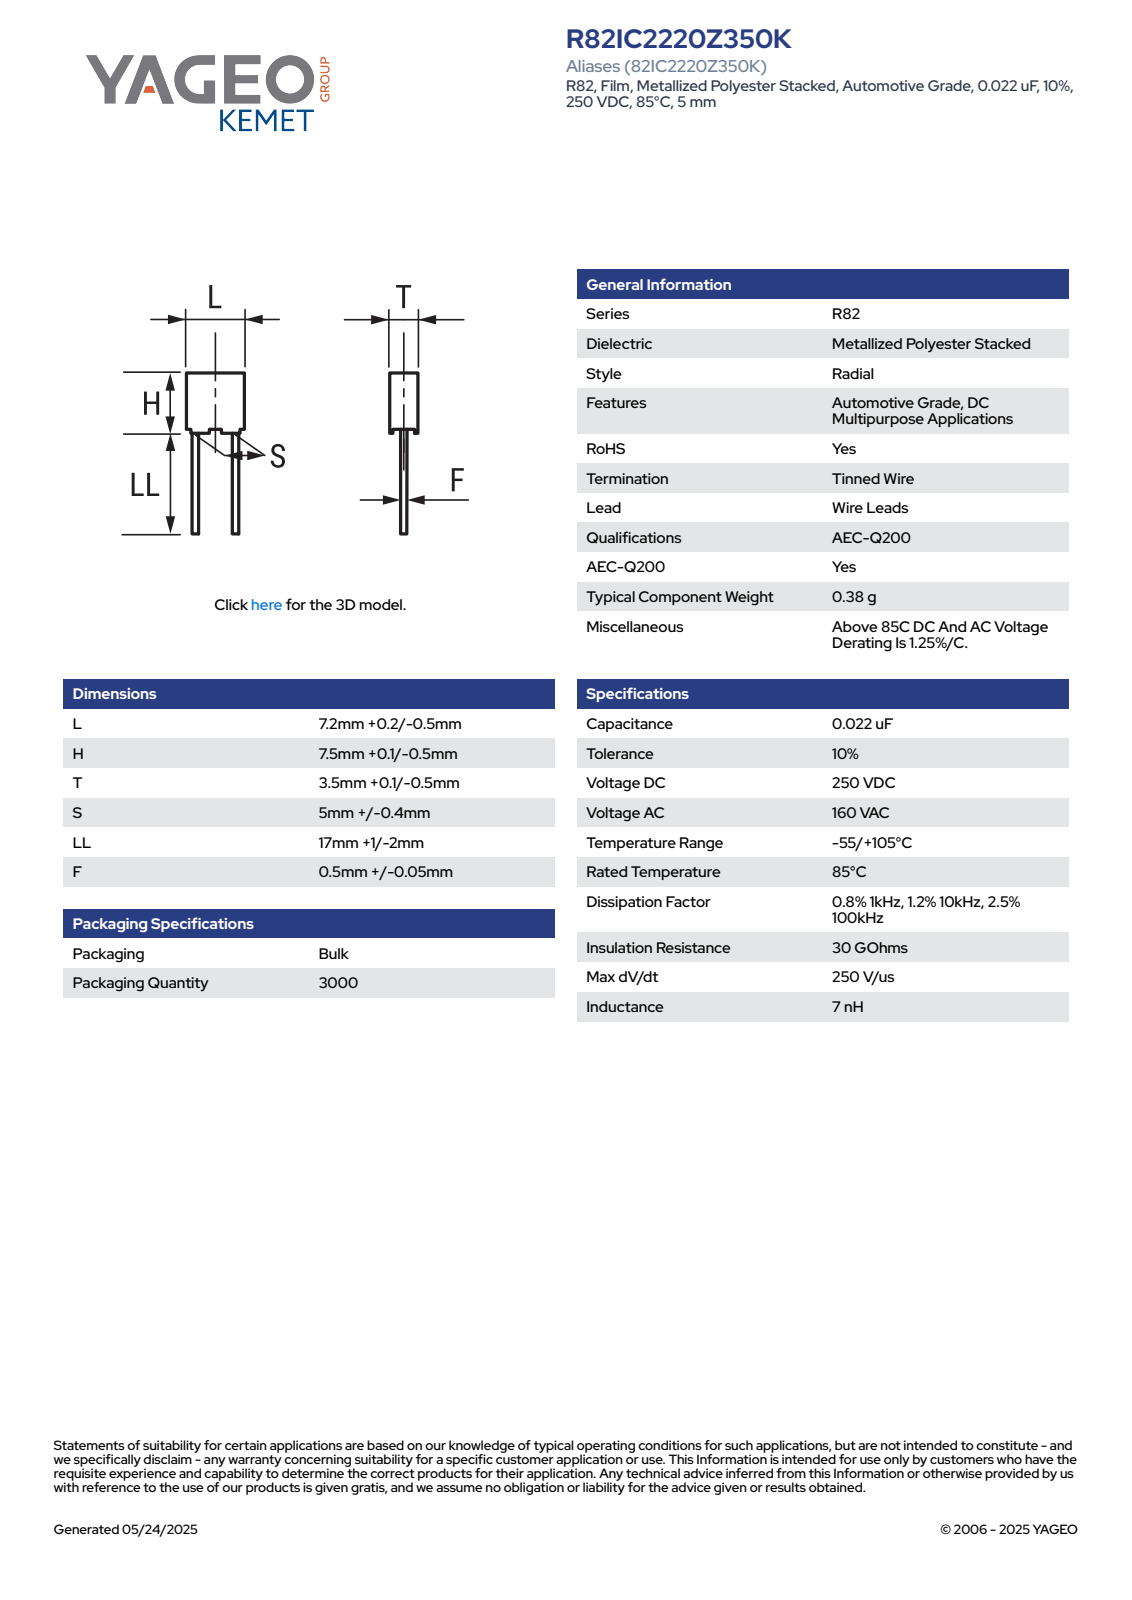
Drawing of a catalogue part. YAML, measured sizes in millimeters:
part_name: "CFR_RB3_7.2X7.5X3.5_L7.4H7.6T3.6S5LL18F0.55"
step_written_by: "SolidWorks 2014 (AUTOMOTIVE_DESIGN)"
units: millimeters
bodies: {solids: 4, faces: 85, planar: 77, cylindrical: 8, other: 0}
overall_size: [25.6, 7.4, 3.6]
volume: 194
surface_area: 298
round_bosses_or_shafts:
  - {diameter: 0.55, count: 2}
partial_cylinders:
  - {radius: 0.5, count: 4}
face_to_face_distances: [3.6, 7.4, 6.85, 3.35, 3.1, 7.15, 0.75, 7.6, 6.9, 0.49]
